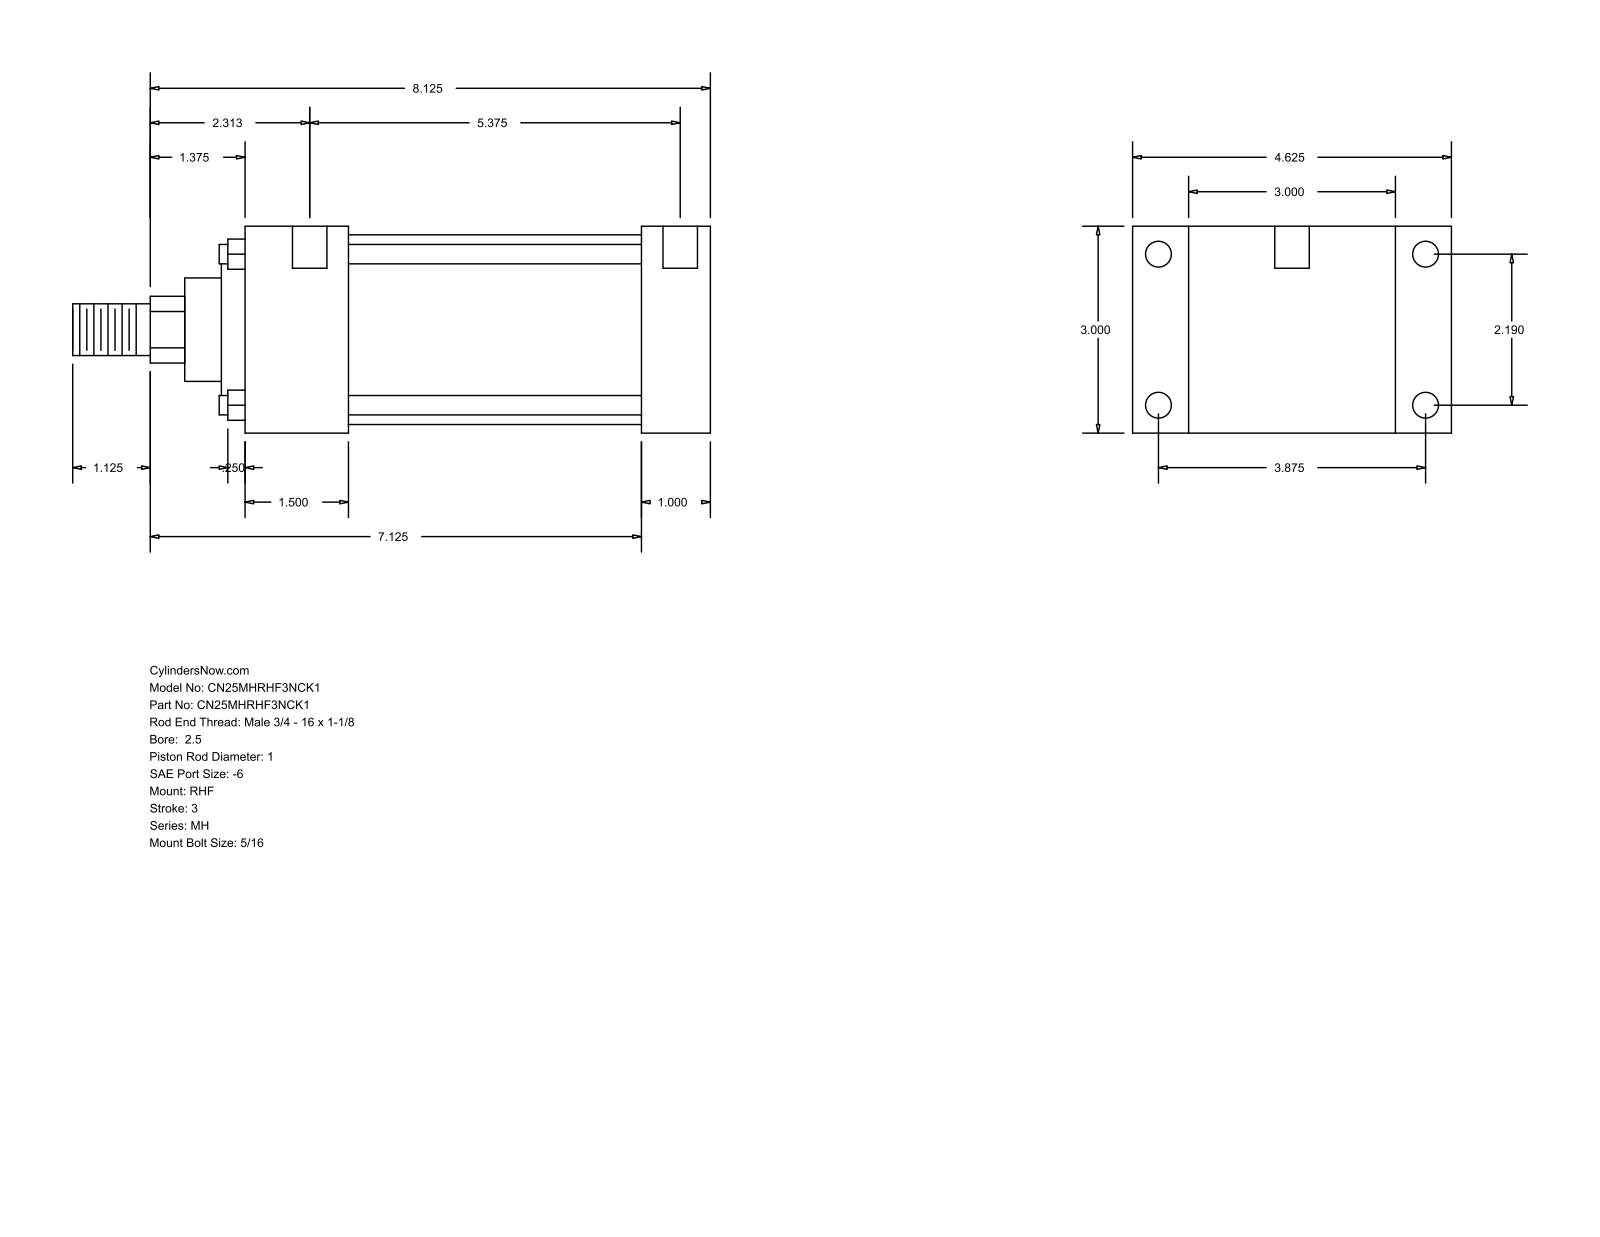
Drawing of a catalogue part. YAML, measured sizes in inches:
part_name: "MH_RHF__0250_1"
step_written_by: "GSSL Pune (CONFIG_CONTROL_DESIGN)"
units: inches
bodies: {solids: 0, faces: 90, planar: 61, cylindrical: 29, other: 0}
overall_size: [9.25, 4.625, 3]
round_holes:
  - {diameter: 0.219, count: 4}
  - {diameter: 0.375, count: 4}
  - {diameter: 0.5, count: 2}
round_bosses_or_shafts:
  - {diameter: 0.281, count: 4}
  - {diameter: 2.75, count: 1}
  - {diameter: 2.375, count: 1}
  - {diameter: 1.5, count: 1}
  - {diameter: 1, count: 1}
  - {diameter: 0.75, count: 1}
partial_cylinders:
  - {radius: 0.484, count: 1}
face_to_face_distances: [3, 1, 0.813, 3.813, 5.75, 6.75, 4.625, 1.5, 4.25, 5.25]
hole_center_spacings: [2.19, 3.875, 4.451, 5.687, 0.125, 0.187, 5.375, 5.5]
